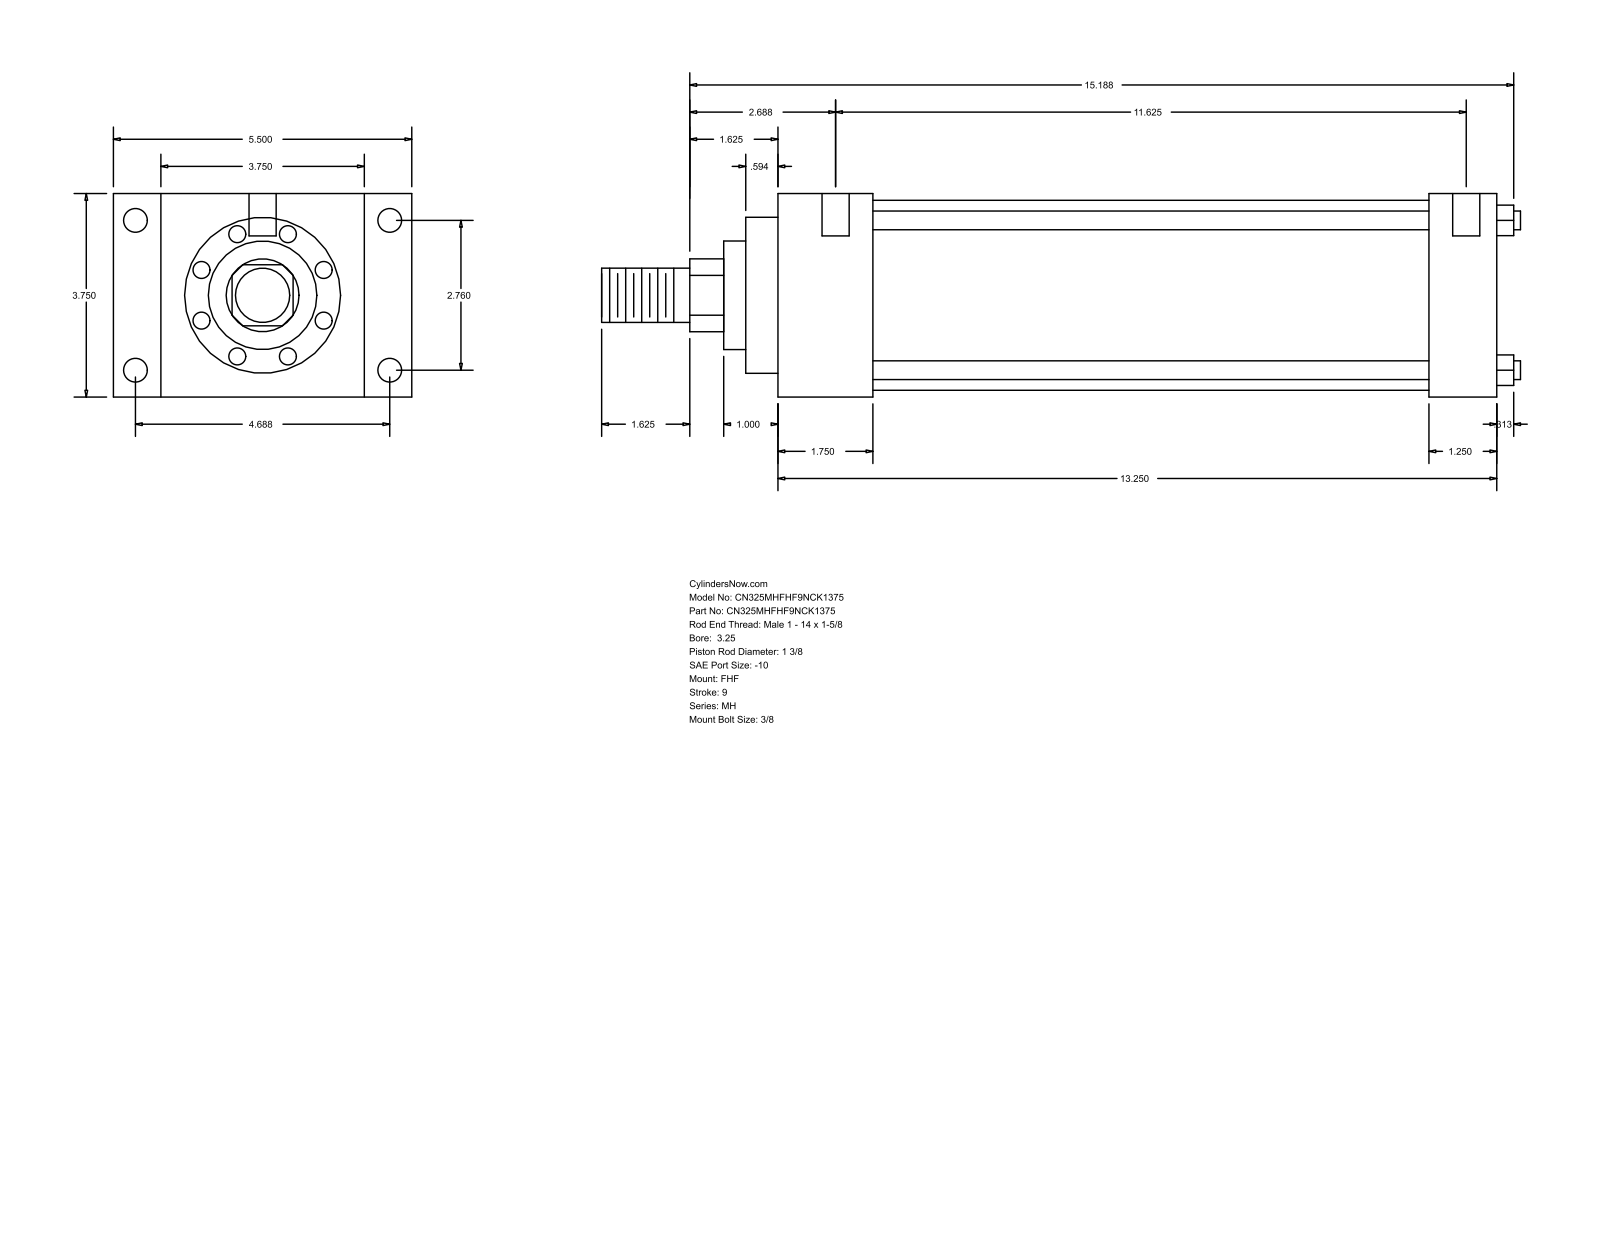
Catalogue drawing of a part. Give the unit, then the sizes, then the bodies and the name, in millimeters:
Units: millimetres
Overall size (bounding box): 430.21 × 139.7 × 95.25
Round holes (diameter × count): ⌀5.56 ×4, ⌀11.13 ×4, ⌀12.7 ×2
Round bosses / shafts (diameter × count): ⌀8.76 ×4, ⌀88.9 ×1, ⌀73.03 ×1, ⌀50.8 ×1, ⌀34.92 ×1, ⌀25.4 ×1
Partial cylindrical surfaces — rounded edges, fillets, slot ends (radius × count): R17.06 ×1
Main face-to-face distances: 95.24, 336.55, 44.45, 292.1, 22.23, 117.47, 139.7, 304.8, 260.35, 31.75
Hole centre spacings: 70.1, 119.06, 138.16, 301.63, 1.59, 4.76, 295.28, 296.87
Bodies: 0 solids, 90 faces (61 planar, 29 cylindrical, 0 other)
Part name (STEP PRODUCT): MH_FHF__0325_1.375
STEP written by: GSSL Pune (CONFIG_CONTROL_DESIGN)
